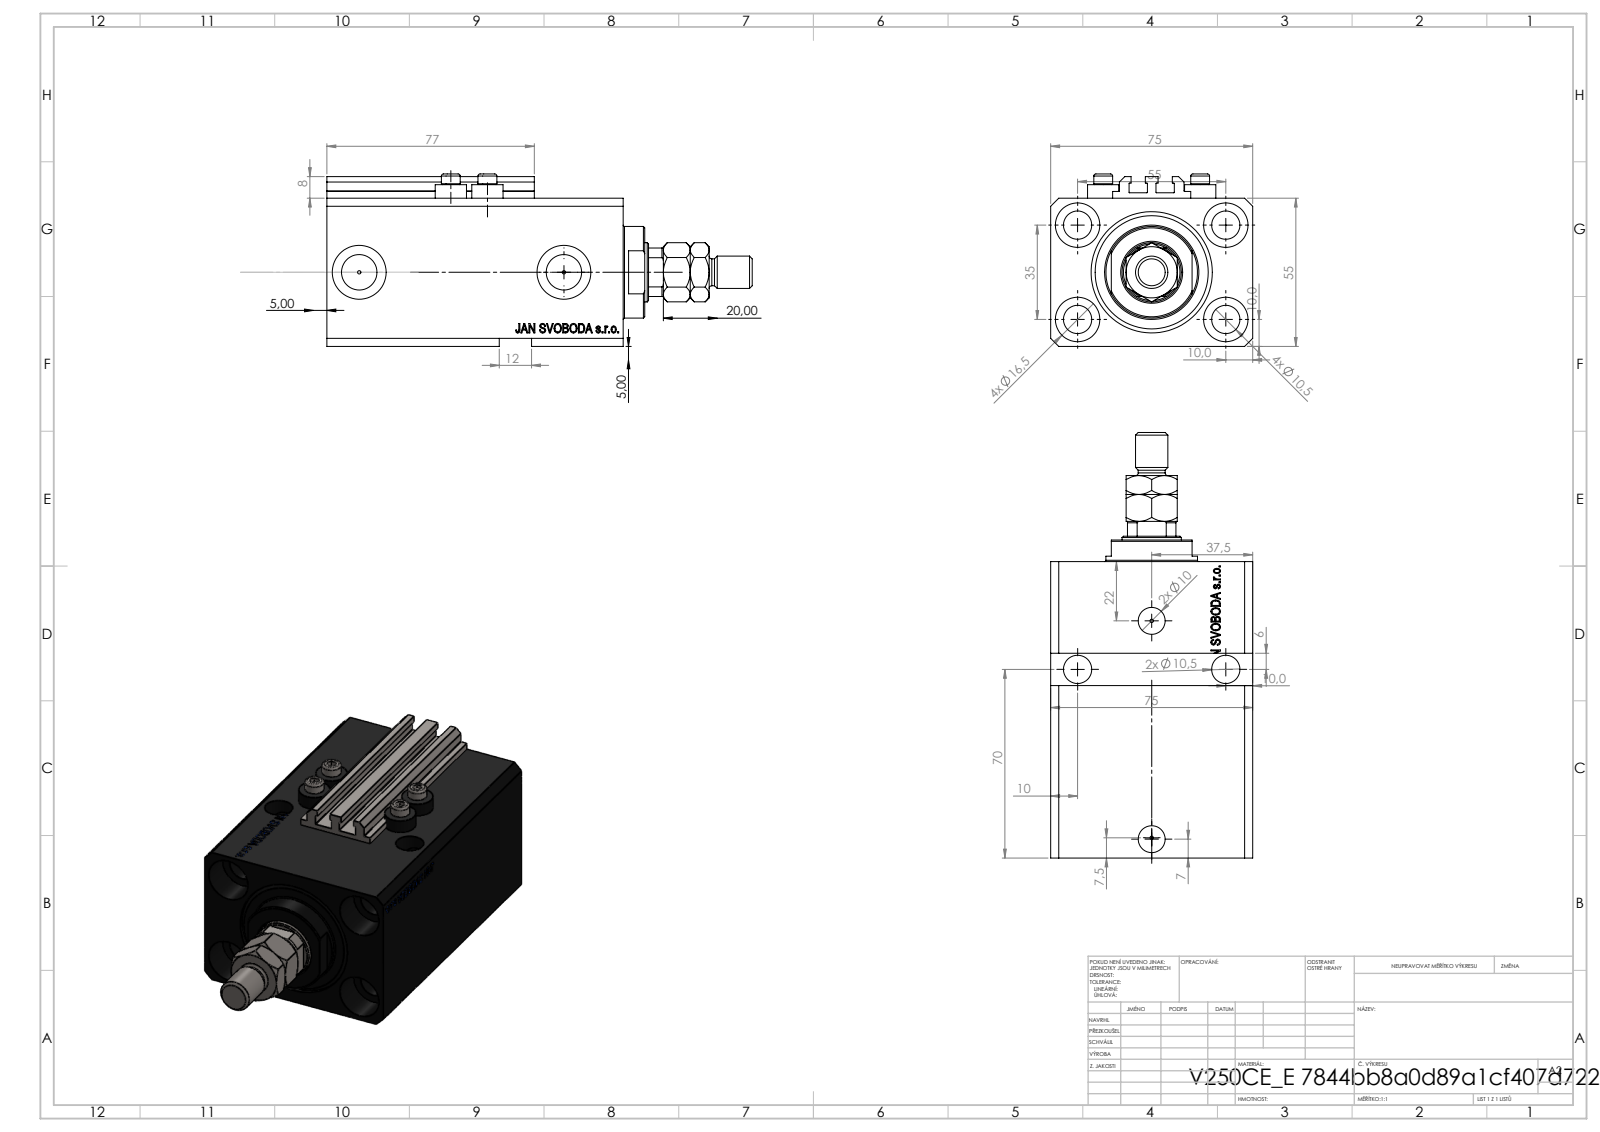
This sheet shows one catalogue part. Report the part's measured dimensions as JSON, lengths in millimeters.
{"part_name": "V250CE_C_VCP; V250CE_E_Body; V250CE_VC_E; MTA (+1 more)", "step_written_by": "SolidWorks 2019 (CONFIG_CONTROL_DESIGN)", "units": "millimeters", "bodies": {"solids": 9, "faces": 1133, "planar": 529, "cylindrical": 150, "other": 454}, "overall_size": [158, 75, 64], "volume_mm3": 388313, "surface_area_mm2": 97960, "round_holes": [[10.5, 9], [1.25, 4], [4, 4], [16.5, 4], [10, 2], [13.16, 2], [20, 2], [22, 1], [32, 1], [45, 1]], "round_bosses_or_shafts": [[11.6, 4], [7, 4], [34, 1], [12, 1], [10, 1]], "partial_cylinders_radius": [[0.2, 10], [10.5, 1]], "face_to_face_distances": [55, 75, 15, 110, 95, 3, 9.9, 85.1, 100.1, 2.5], "hole_center_spacings": [32.6, 32.87, 55, 68.74, 13.6, 14.09, 23.05, 25.81]}
